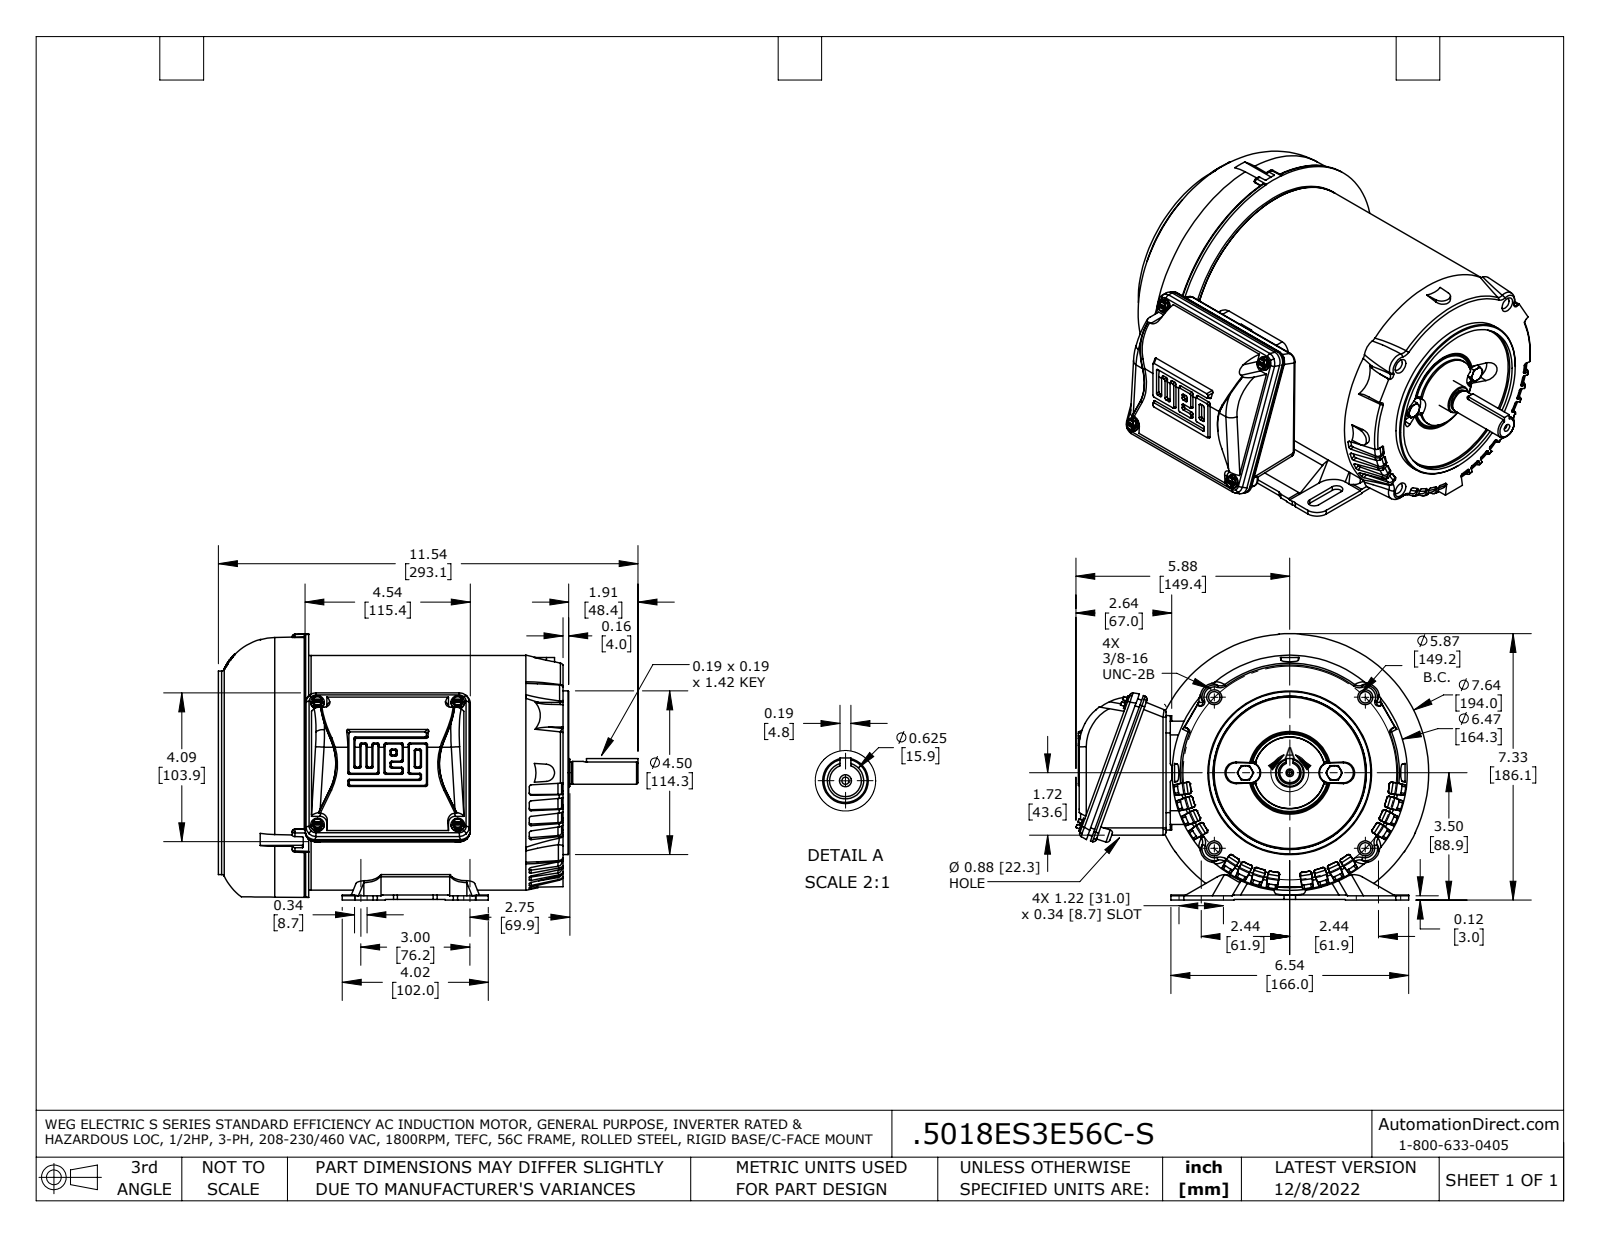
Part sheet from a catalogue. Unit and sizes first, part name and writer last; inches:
Units: inches
Overall size (bounding box): 11.539 × 9.7 × 7.551
Round holes (diameter × count): ⌀0.313 ×4, ⌀0.124 ×1
Round bosses / shafts (diameter × count): ⌀0.374 ×4, ⌀0.35 ×2, ⌀6.447 ×1, ⌀6.447 ×1, ⌀5.591 ×1, ⌀4.5 ×1, ⌀0.783 ×1, ⌀0.625 ×1
Partial cylindrical surfaces — rounded edges, fillets, slot ends (radius × count): R0.047 ×40, R0.006 ×38, R0.051 ×32, R0.059 ×12, R0.079 ×12, R0.087 ×12, R0.02 ×10, R0.171 ×8
Main face-to-face distances: 5.906, 0.067, 5.972, 2.283, 2.35, 8.256, 9.28, 6.996, 6.929, 1.024
Hole centre spacings: 2.937, 4.154, 5.874
Volume: 359 in³ · Surface area: 650 in²
Bodies: 14 solids, 1418 faces (539 planar, 331 cylindrical, 548 other)
Part name (STEP PRODUCT): 56C_3PH_TEFC_GP_11535 fxt
STEP written by: SolidWorks 2021 (AUTOMOTIVE_DESIGN)
